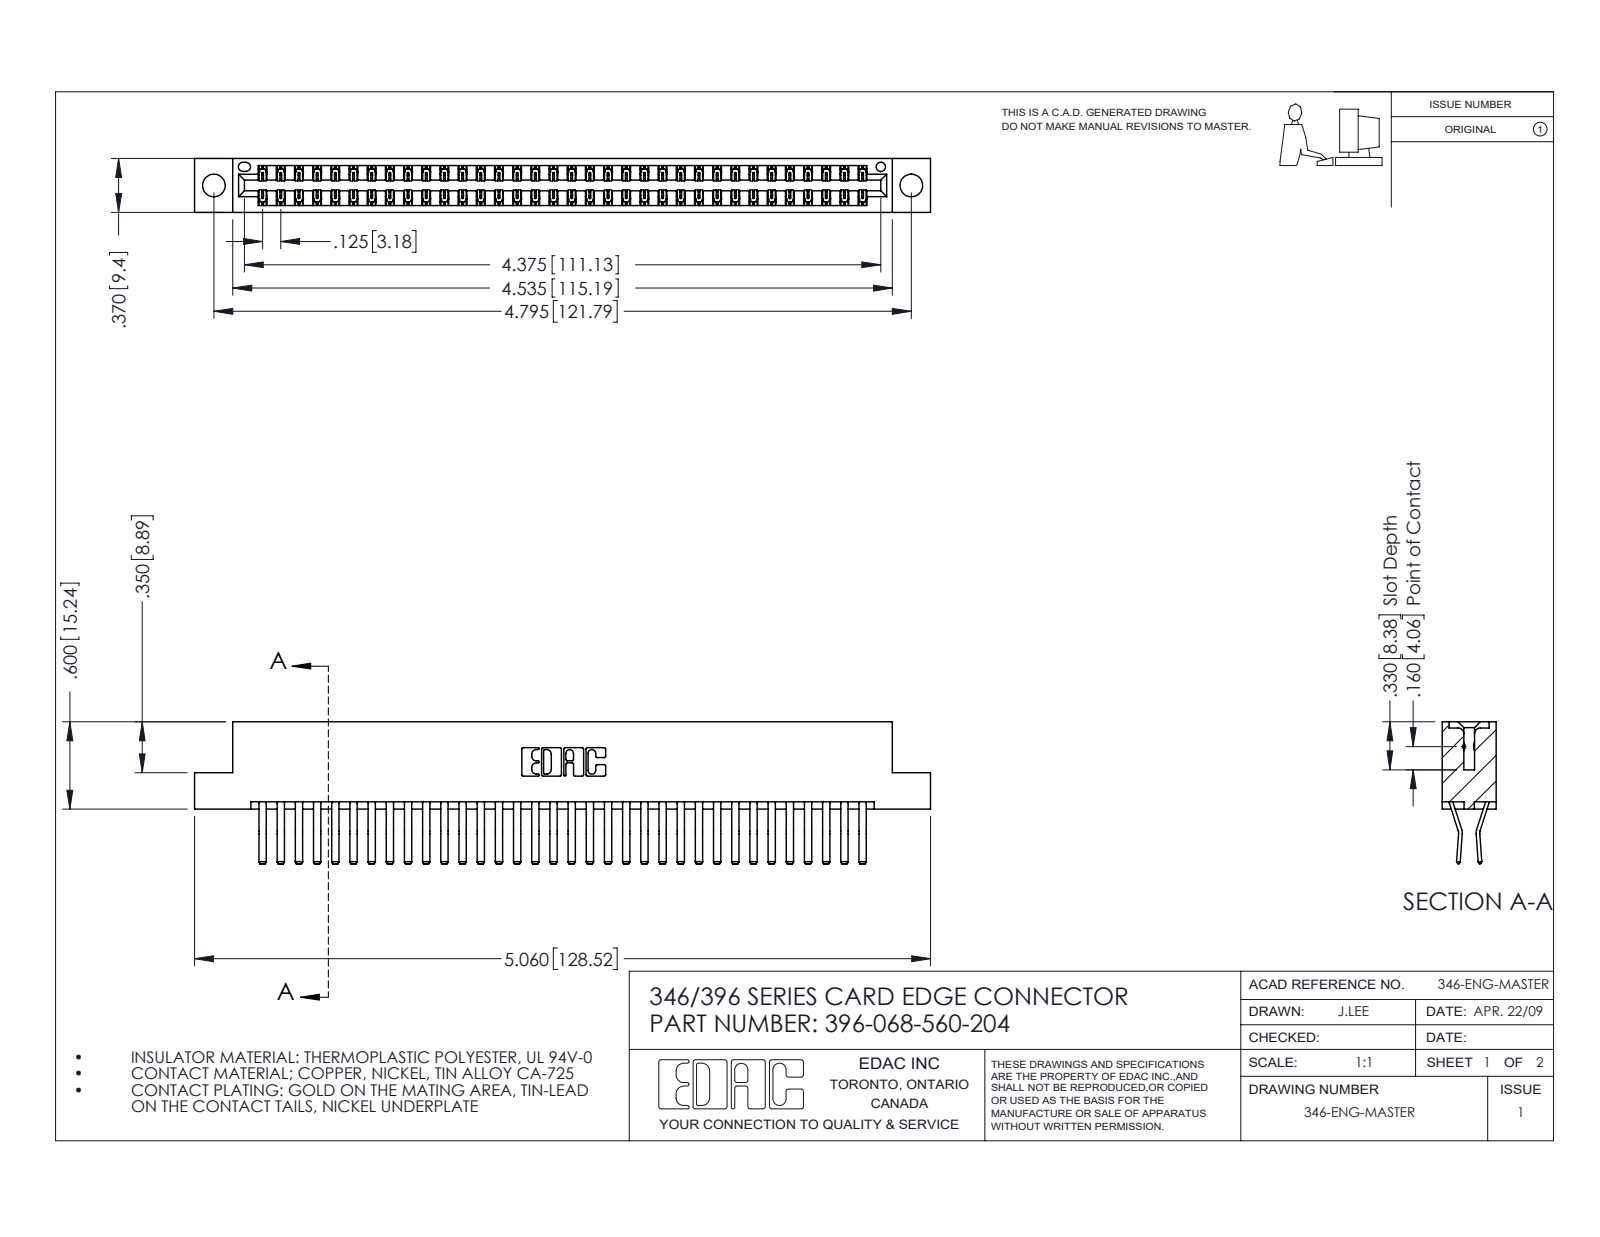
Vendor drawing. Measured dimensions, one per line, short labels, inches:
name: 396-068-560-204; 346 Part_Flush Mounting Lugs - 0.156 Dia-TH; 345-292-001_560 Tail
written by: SolidWorks 2016 (CONFIG_CONTROL_DESIGN)
unit: in
bodies: 69 solids, 3794 faces (2456 planar, 1338 cylindrical, 0 other)
size: 5.06 × 0.975 × 0.37
volume: 0.783 in³; area: 28.69 in²
holes: 2× ⌀0.156, 1× ⌀0.064
rounds: 102× R0.006, 22× R0.01, 6× R0.007, 6× R0.031, 3× R0.026, 2× R0.01, 2× R0.014, 2× R0.022
face distances: 0.048, 0.322, 0.37, 0.025, 0.25, 0.072, 0.298, 0.275, 0.148, 0.222
hole spacings: 0.246, 4.587, 4.795
